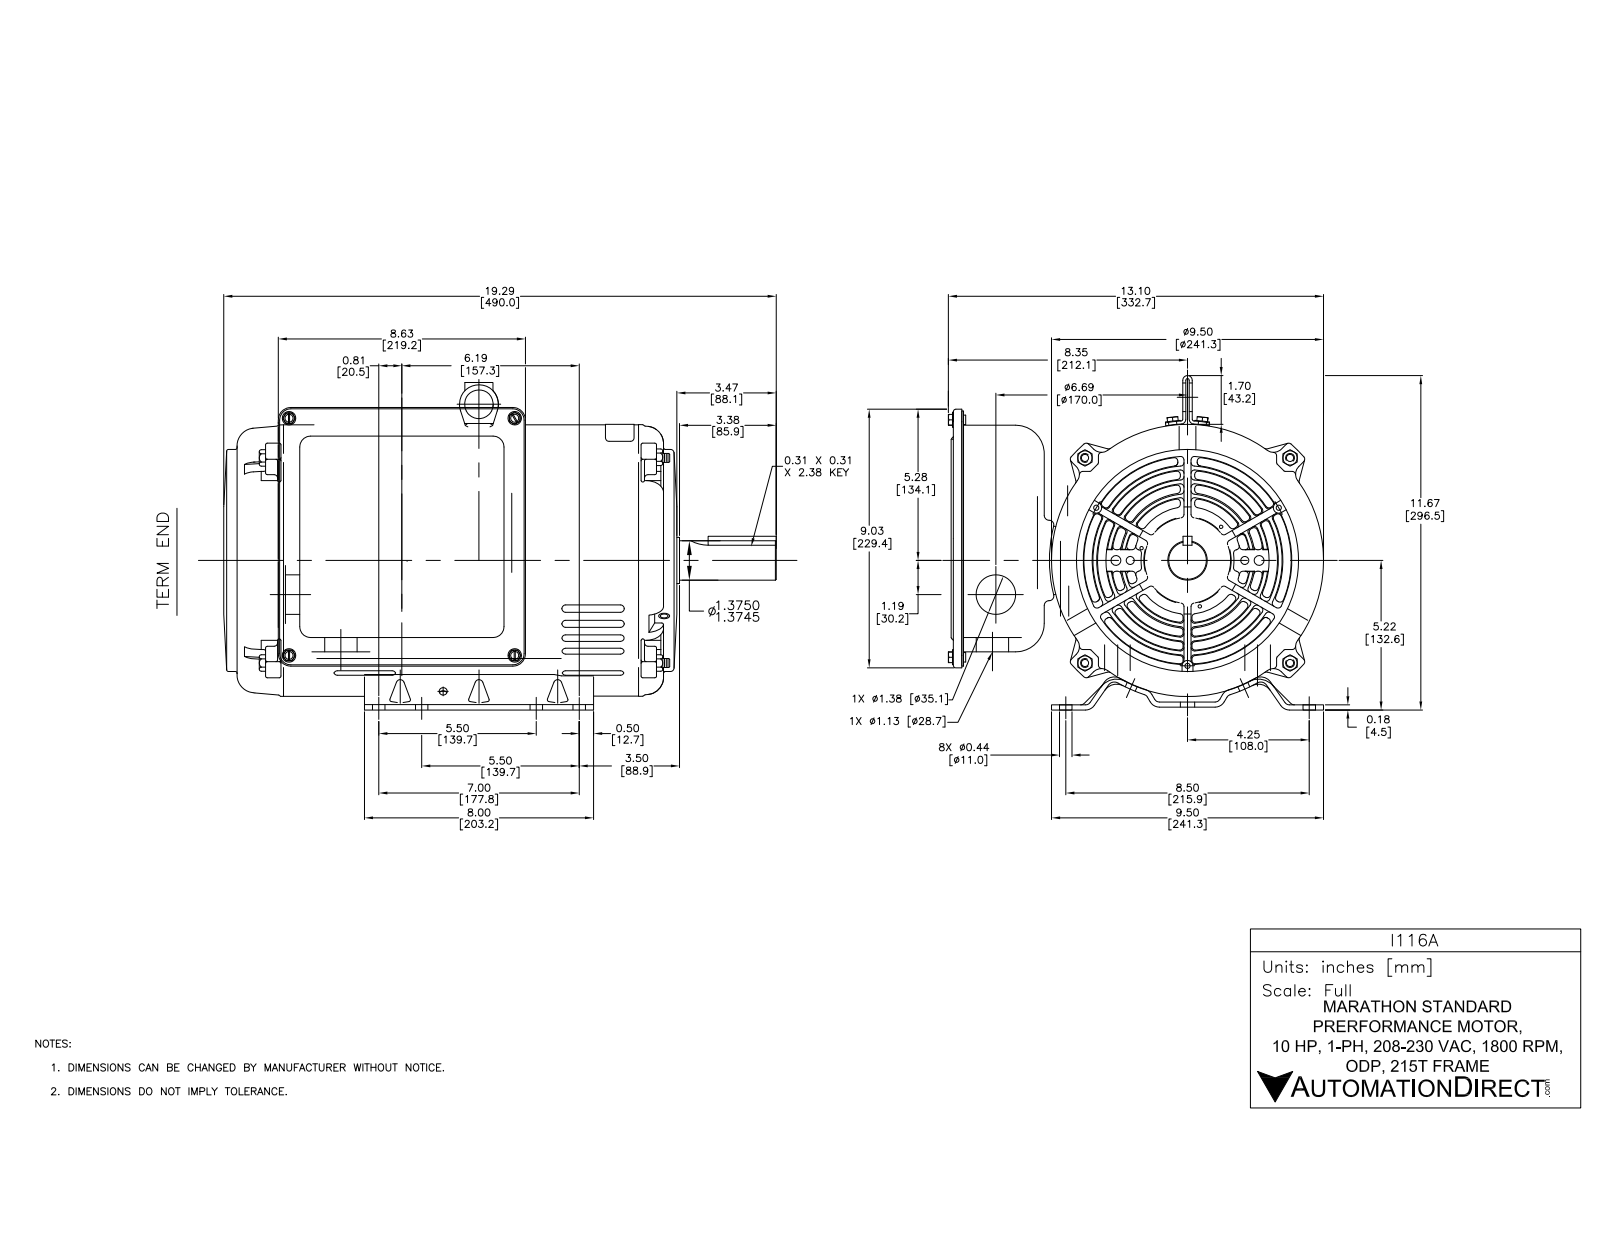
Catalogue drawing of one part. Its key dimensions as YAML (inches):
part_name: "I116 SS88686-1240_Rev0"
step_written_by: "SolidWorks 2017 (AUTOMOTIVE_DESIGN)"
units: inches
bodies: {solids: 32, faces: 3602, planar: 1339, cylindrical: 763, other: 1500}
overall_size: [19.388, 12.875, 11.642]
volume: 166.7
surface_area: 2171
round_holes:
  - {diameter: 0.373, count: 10}
  - {diameter: 0.219, count: 8}
  - {diameter: 0.153, count: 6}
  - {diameter: 0.435, count: 6}
  - {diameter: 0.28, count: 5}
  - {diameter: 0.213, count: 4}
  - {diameter: 0.257, count: 4}
  - {diameter: 0.3, count: 4}
  - {diameter: 0.125, count: 3}
  - {diameter: 0.175, count: 3}
  - {diameter: 0.1, count: 2}
  - {diameter: 0.279, count: 2}
round_bosses_or_shafts:
  - {diameter: 0.25, count: 9}
  - {diameter: 0.52, count: 7}
  - {diameter: 0.331, count: 4}
  - {diameter: 0.31, count: 4}
  - {diameter: 0.68, count: 2}
  - {diameter: 0.5, count: 2}
  - {diameter: 0.38, count: 2}
  - {diameter: 0.35, count: 2}
partial_cylinders:
  - {radius: 0.135, count: 72}
  - {radius: 0.06, count: 39}
  - {radius: 0.03, count: 36}
  - {radius: 0.25, count: 34}
  - {radius: 0.12, count: 26}
  - {radius: 0.19, count: 11}
  - {radius: 0.309, count: 10}
  - {radius: 0.429, count: 8}
face_to_face_distances: [0.059, 0.036, 0.179, 0.111, 7.441, 0.075, 0.11, 0.036, 0.039, 0.075]
hole_center_spacings: [2.5, 1, 1.5, 1.75, 3.5, 3.737, 3.911, 4.072]
